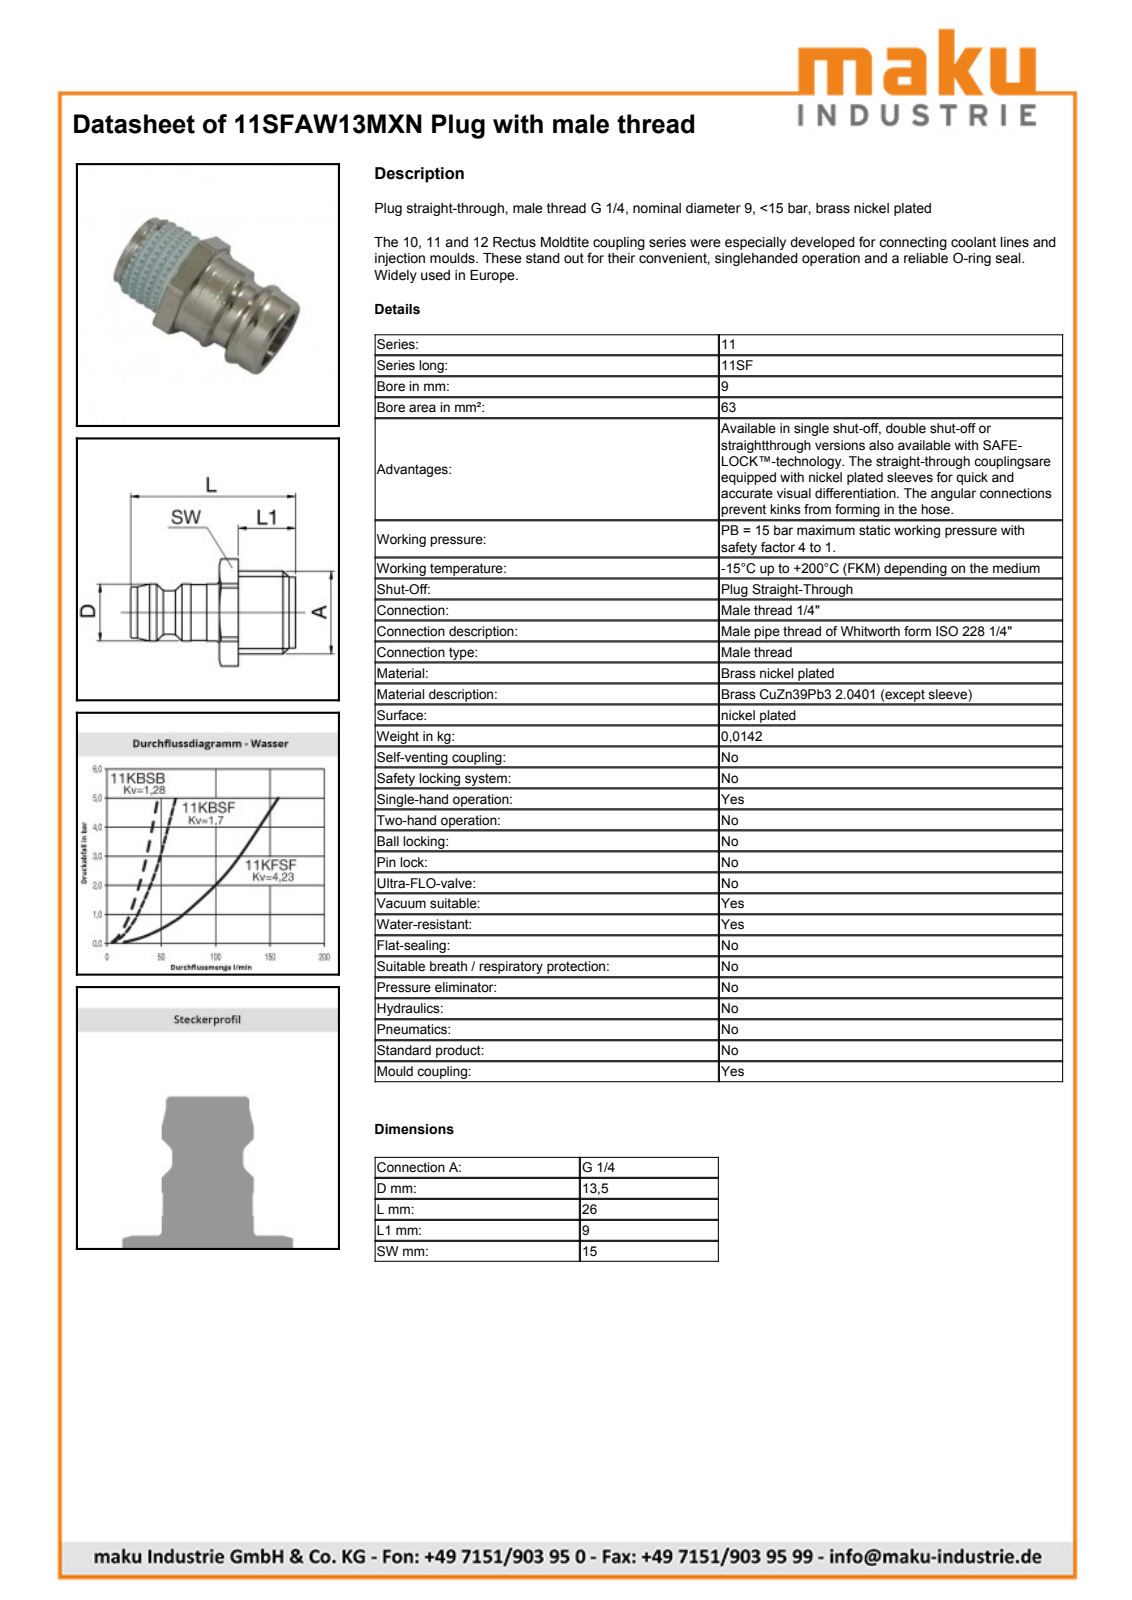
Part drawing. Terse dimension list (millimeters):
name: D112458
written by: Autodesk Inventor 2013 (AUTOMOTIVE_DESIGN)
unit: mm
bodies: 1 solid, 43 faces (13 planar, 14 cylindrical, 16 other)
size: 25.9 × 16.9 × 15
volume: 3 492 mm³; area: 1 441 mm²
bosses: 1× ⌀13.5, 1× ⌀13.3, 1× ⌀13.16, 1× ⌀12.5, 1× ⌀11.2, 1× ⌀10.8
rounds: 1× R8.45
face distances: 25.9, 15, 16.9, 9, 14, 2.9, 11.9, 12.5, 1.5, 4.4
